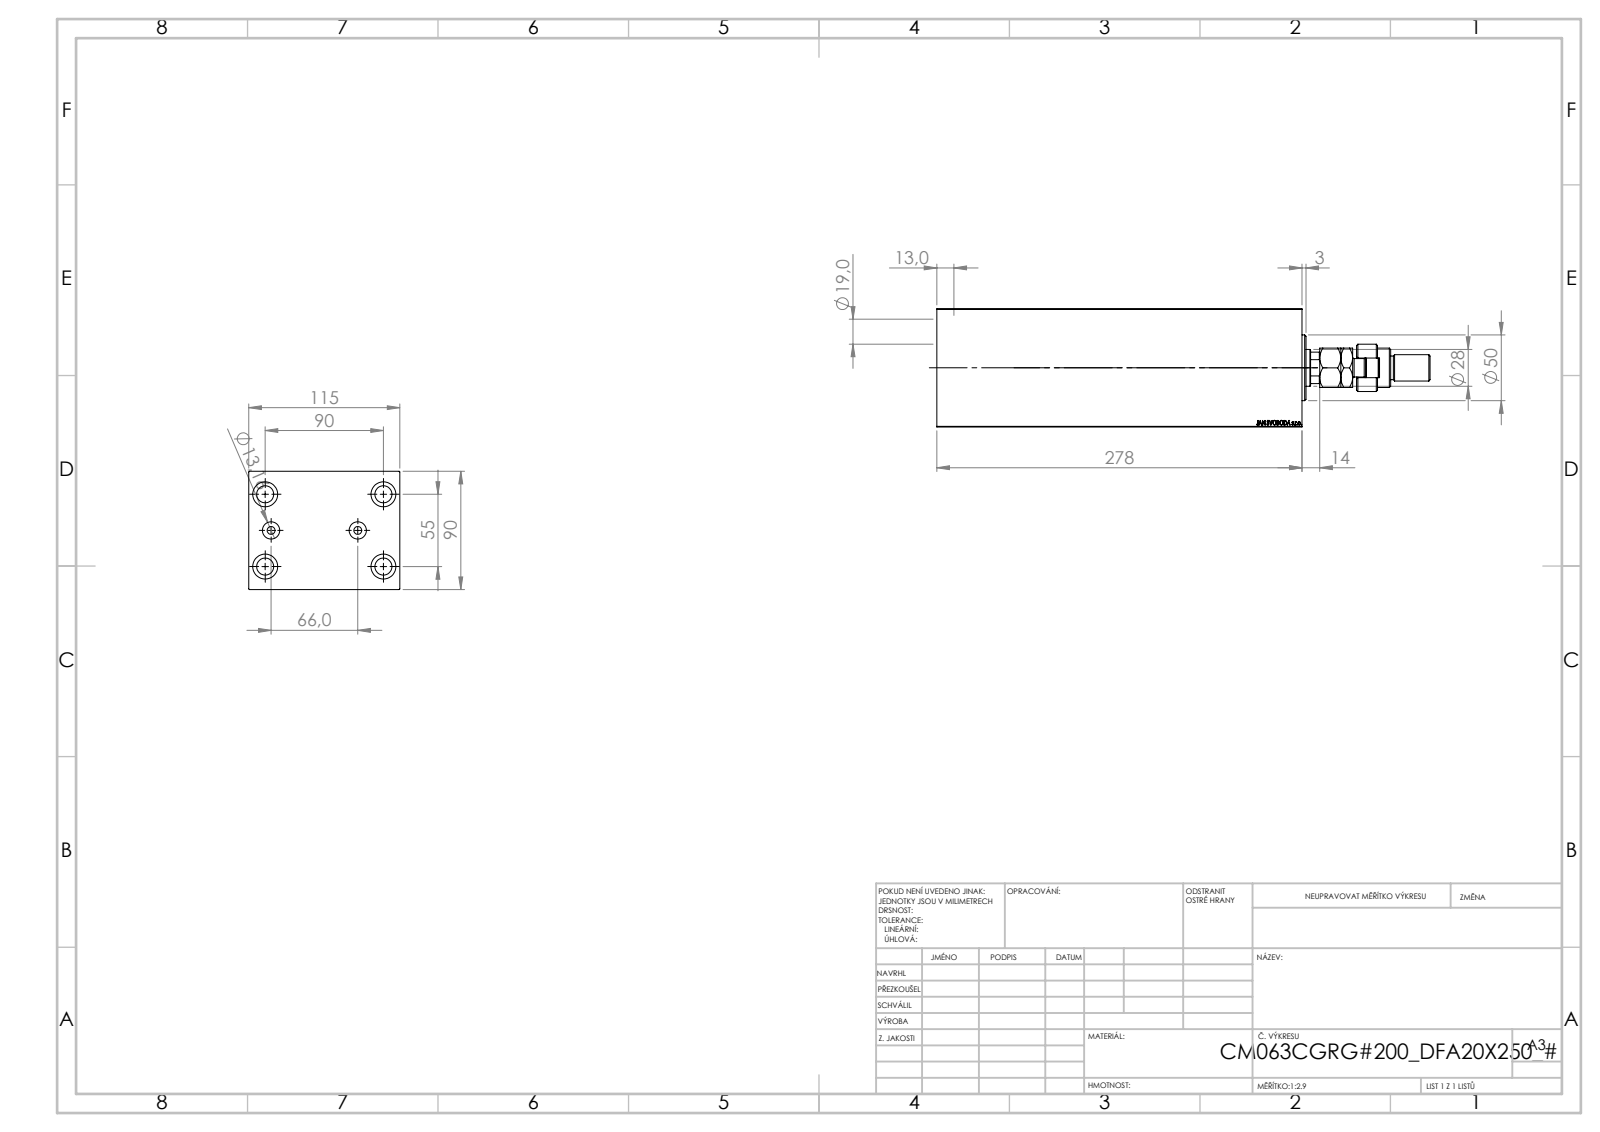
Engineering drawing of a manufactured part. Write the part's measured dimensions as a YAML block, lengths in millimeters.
part_name: "V450CM_C_VCP; V450CM_VC_B; V450CM_C_Body; FEMALE_PART_FOR_DFA (+1 more)"
step_written_by: "SolidWorks 2019 (CONFIG_CONTROL_DESIGN)"
units: millimeters
bodies: {solids: 5, faces: 946, planar: 437, cylindrical: 71, other: 438}
overall_size: [375.5, 115, 90]
volume: 2252000
surface_area: 302013
round_holes:
  - {diameter: 13, count: 4}
  - {diameter: 19, count: 4}
  - {diameter: 6, count: 2}
  - {diameter: 13.16, count: 2}
  - {diameter: 18.5, count: 1}
  - {diameter: 28, count: 1}
  - {diameter: 31.5, count: 1}
  - {diameter: 63, count: 1}
  - {diameter: 65, count: 1}
  - {diameter: 72, count: 1}
round_bosses_or_shafts:
  - {diameter: 50, count: 1}
  - {diameter: 36, count: 1}
  - {diameter: 30, count: 1}
  - {diameter: 22, count: 1}
  - {diameter: 20, count: 1}
  - {diameter: 18, count: 1}
  - {diameter: 14, count: 1}
partial_cylinders:
  - {radius: 7.5, count: 1}
  - {radius: 12, count: 1}
  - {radius: 13.5, count: 1}
face_to_face_distances: [90, 115, 278, 17.5, 260.5, 29.3, 231.2, 248.7, 229.3, 200]
hole_center_spacings: [30, 52.74, 82.71, 33, 55, 90, 105.48, 66]
